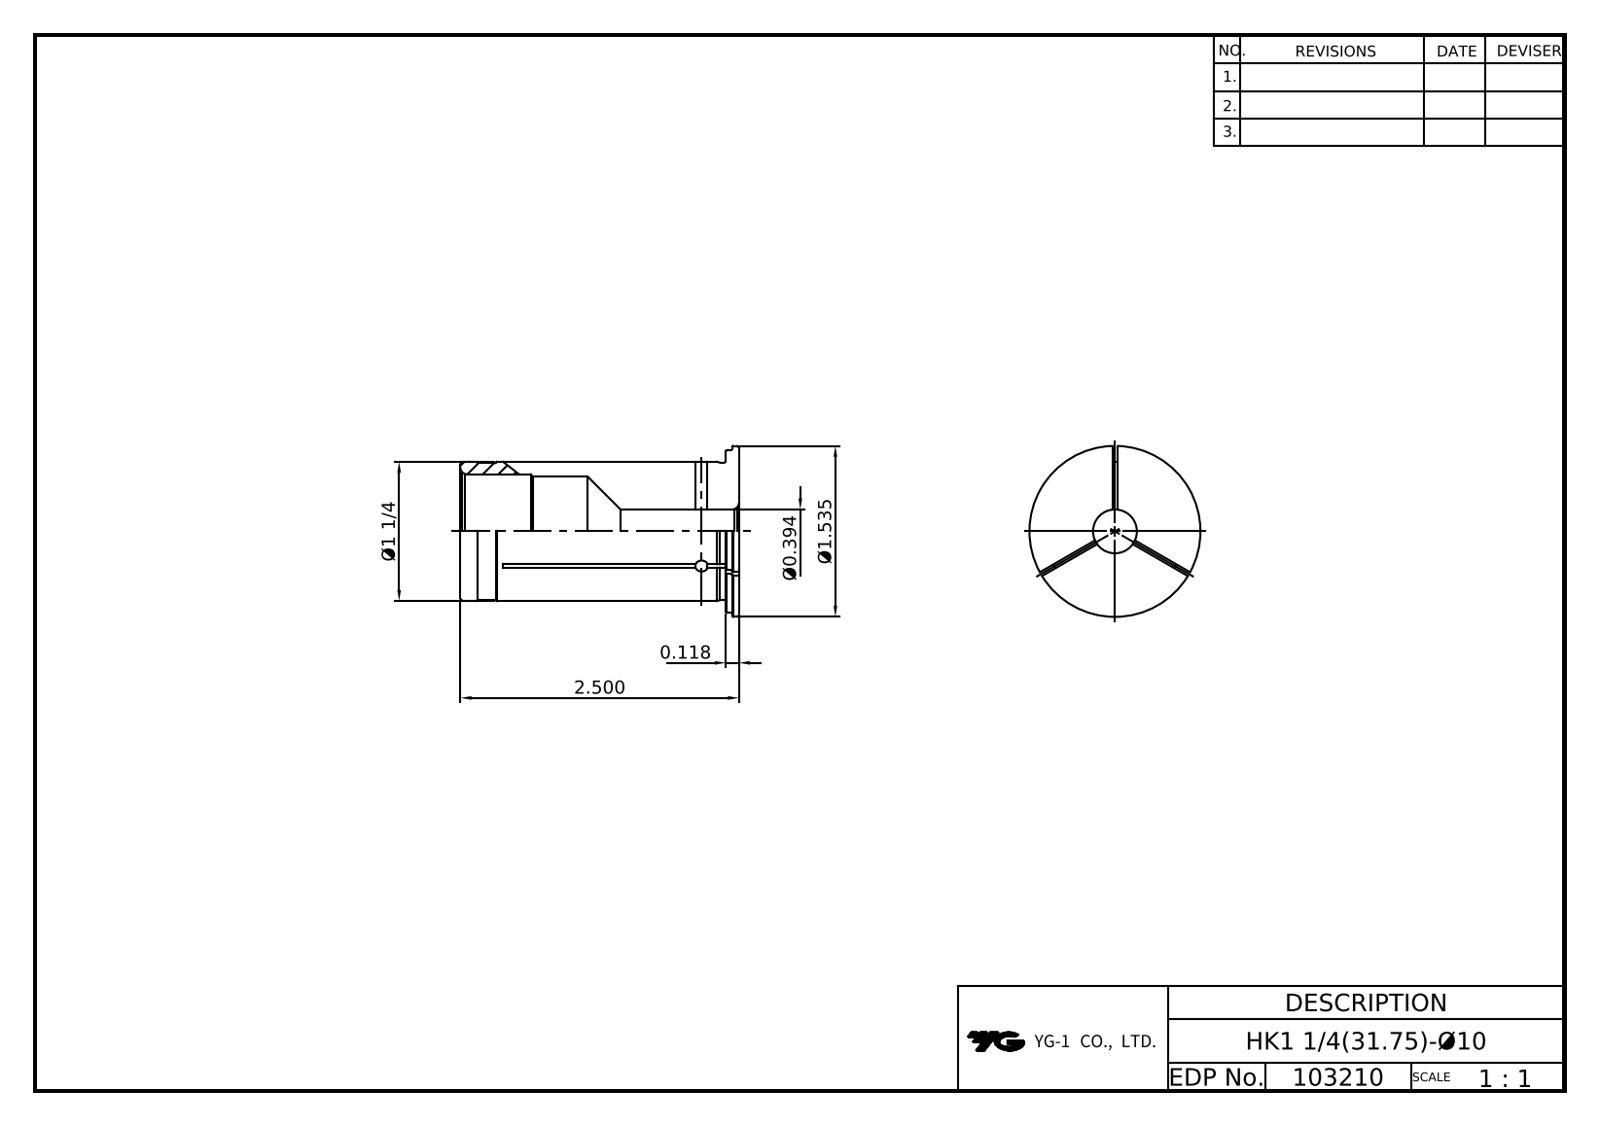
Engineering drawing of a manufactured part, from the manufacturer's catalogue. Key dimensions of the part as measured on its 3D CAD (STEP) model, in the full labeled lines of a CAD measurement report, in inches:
Part name (STEP PRODUCT): LO-HK31.75-10
STEP written by: Autodesk Inventor 2025 (AP242_MANAGED_MODEL_BASED_3D_ENGINEERING_MIM_LF)
Units: inches
Bodies: 1 solid, 16 faces (4 planar, 6 cylindrical, 6 other)
Overall size (bounding box): 2.5 × 1.535 × 1.535
Volume: 1.976 in³ · Surface area: 18.41 in²
Round holes (diameter × count): ⌀0.394 ×1, ⌀0.984 ×1, ⌀1.024 ×1
Round bosses / shafts (diameter × count): ⌀1.535 ×1, ⌀1.457 ×1, ⌀1.25 ×1
Main face-to-face distances: 2.5, 2.382, 0.118, 0.059, 2.441
